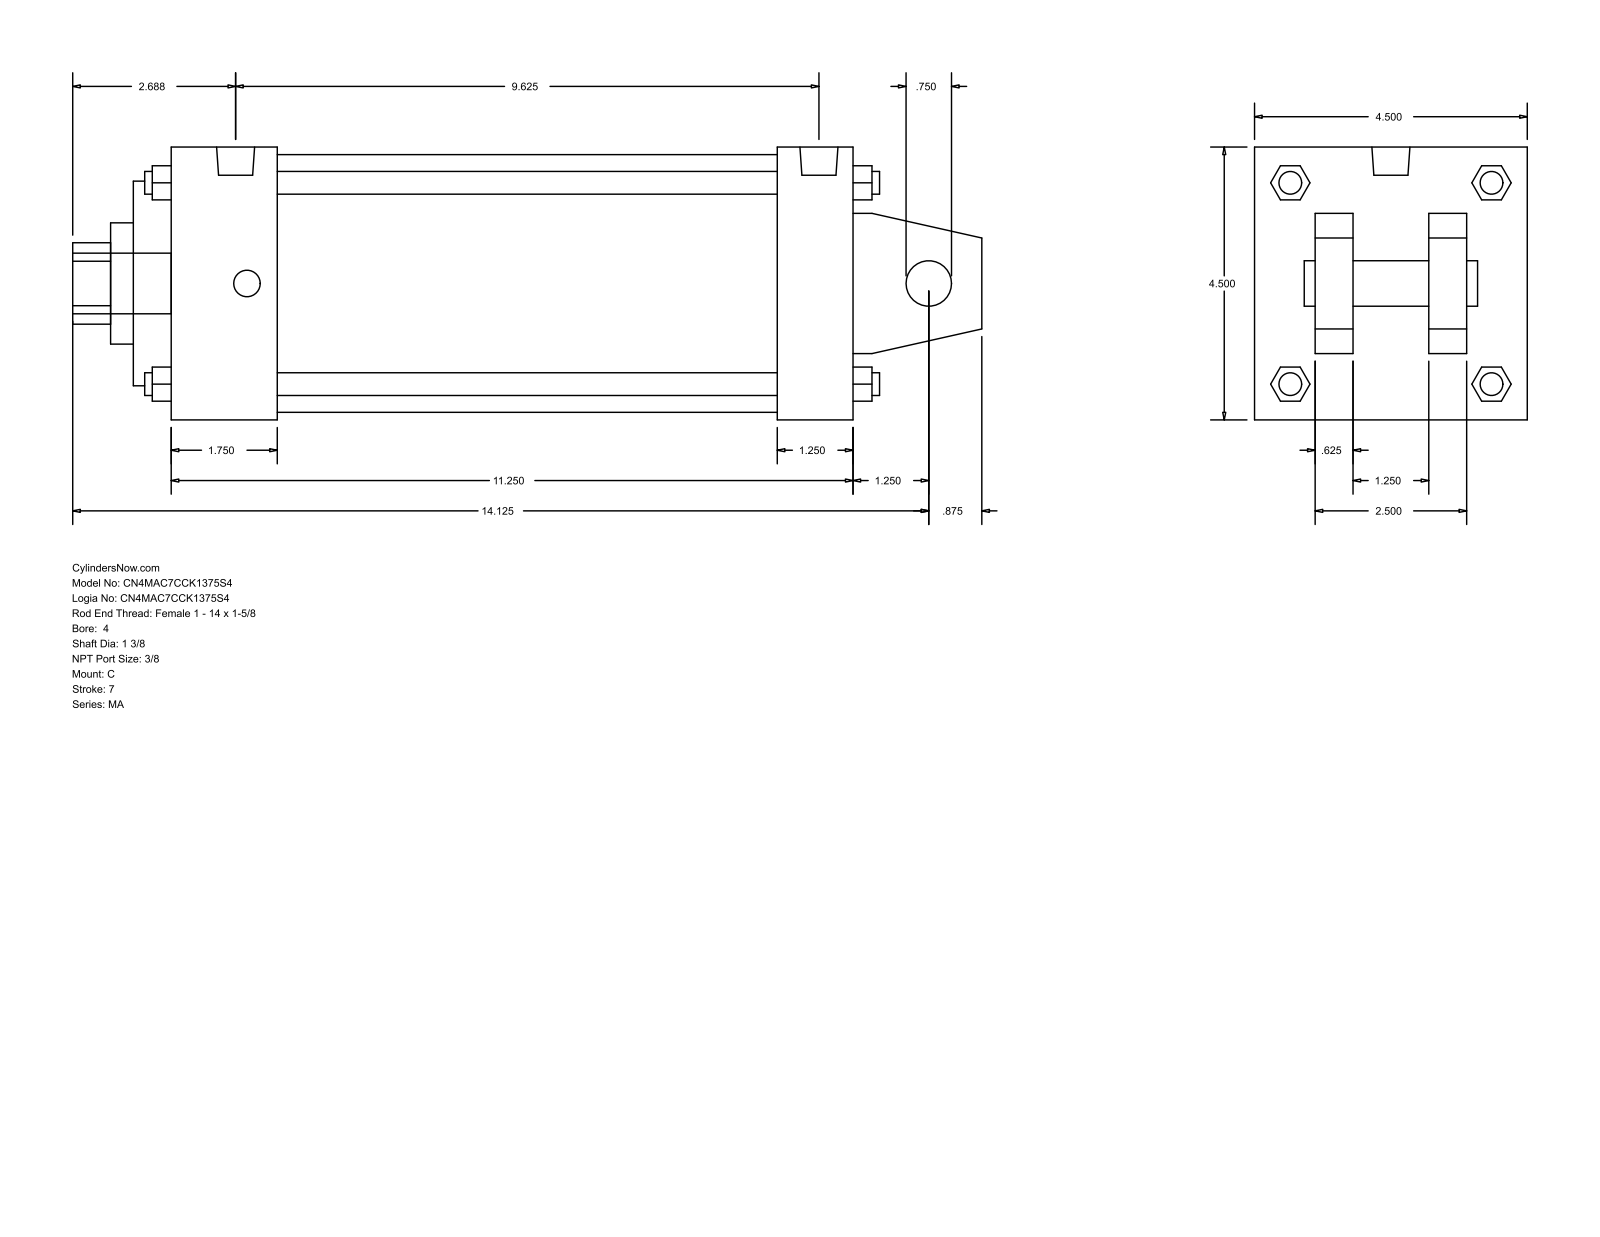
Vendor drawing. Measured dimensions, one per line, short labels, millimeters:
name: MA_C__0400_1.375
written by: GSSL Pune (CONFIG_CONTROL_DESIGN)
unit: mm
bodies: 0 solids, 141 faces (109 planar, 32 cylindrical, 0 other)
size: 381 × 114.3 × 114.3
holes: 1× ⌀19.05, 1× ⌀34.92, 1× ⌀50.8, 1× ⌀85.72, 1× ⌀107.95
bosses: 4× ⌀11.11, 4× ⌀9.53, 2× ⌀15.93, 1× ⌀25.4
rounds: 1× R17.06
face distances: 114.3, 15.87, 285.75, 73.03, 41.27, 25.4, 88.9, 47.63, 301.62, 269.87
